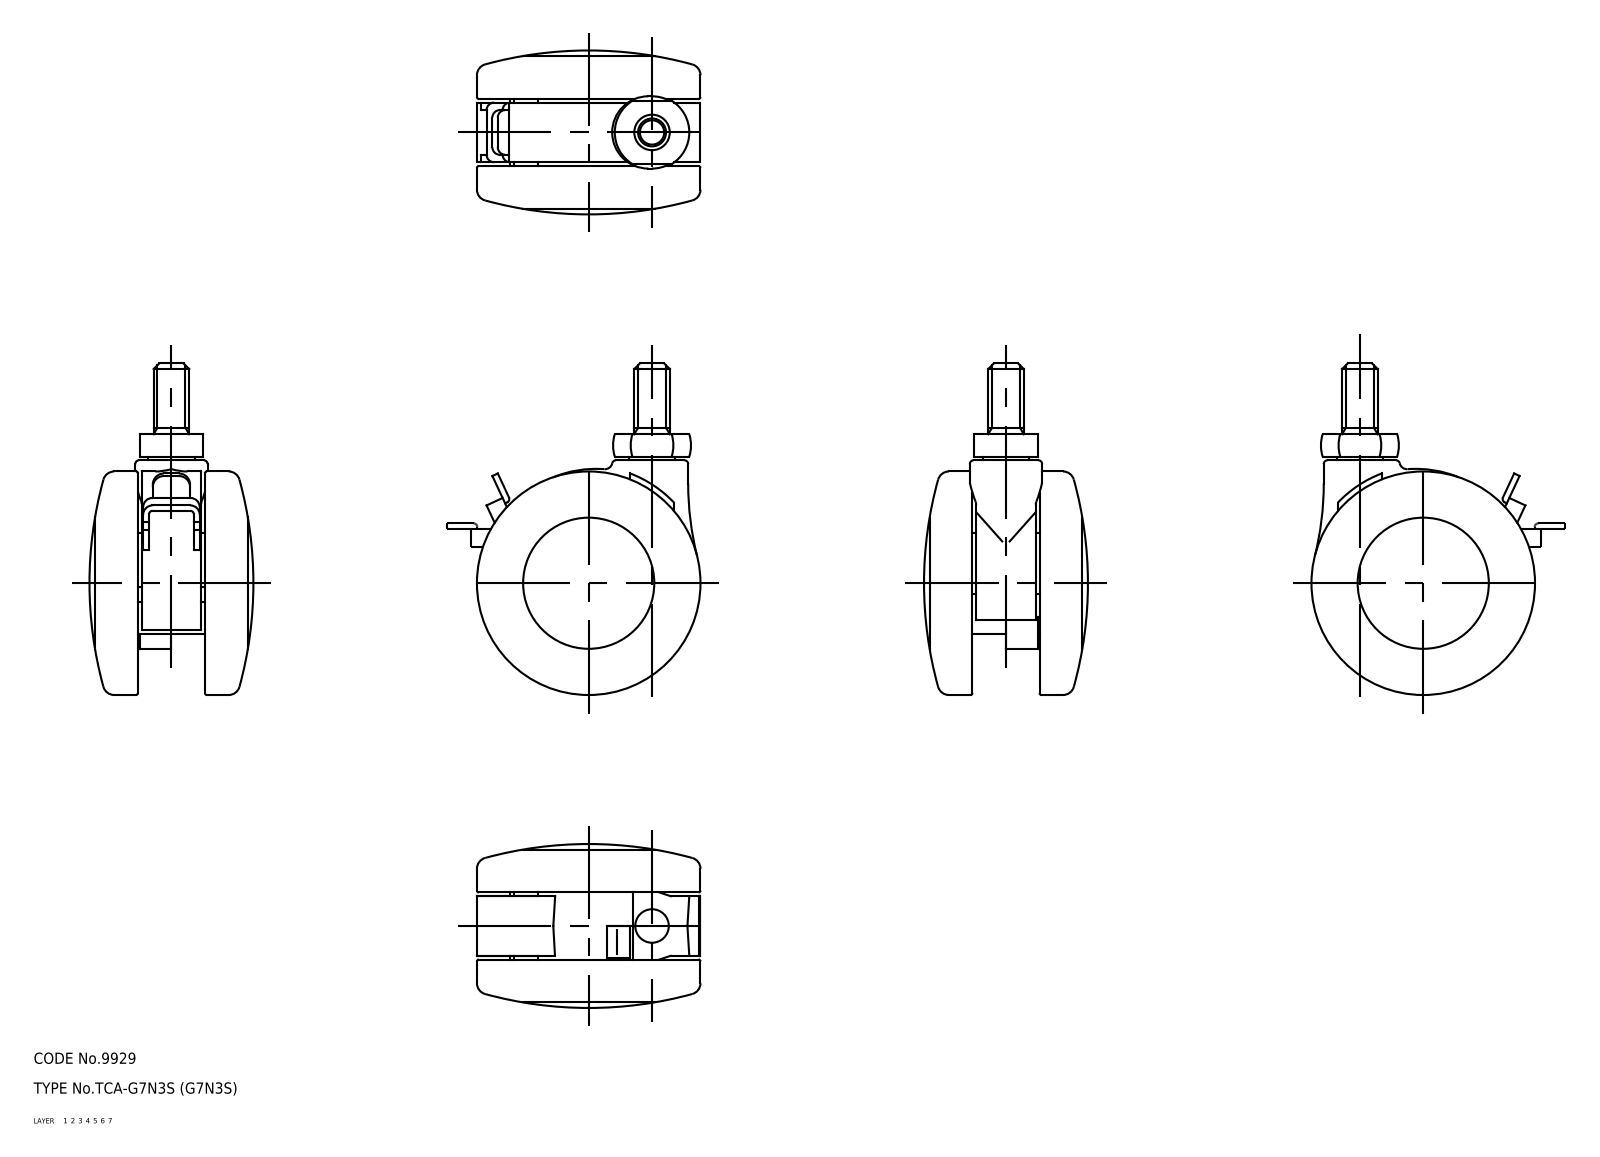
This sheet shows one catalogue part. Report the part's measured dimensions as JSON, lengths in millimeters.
{"part_name": "wheel; main shaft; lever; G7N3S_13233_36", "step_written_by": "CADfix (AUTOMOTIVE_DESIGN)", "units": "millimeters", "bodies": {"solids": 5, "faces": 194, "planar": 0, "cylindrical": 0, "other": 194}, "overall_size": [89, 68, 44], "volume_mm3": 92802, "surface_area_mm2": 34194}
